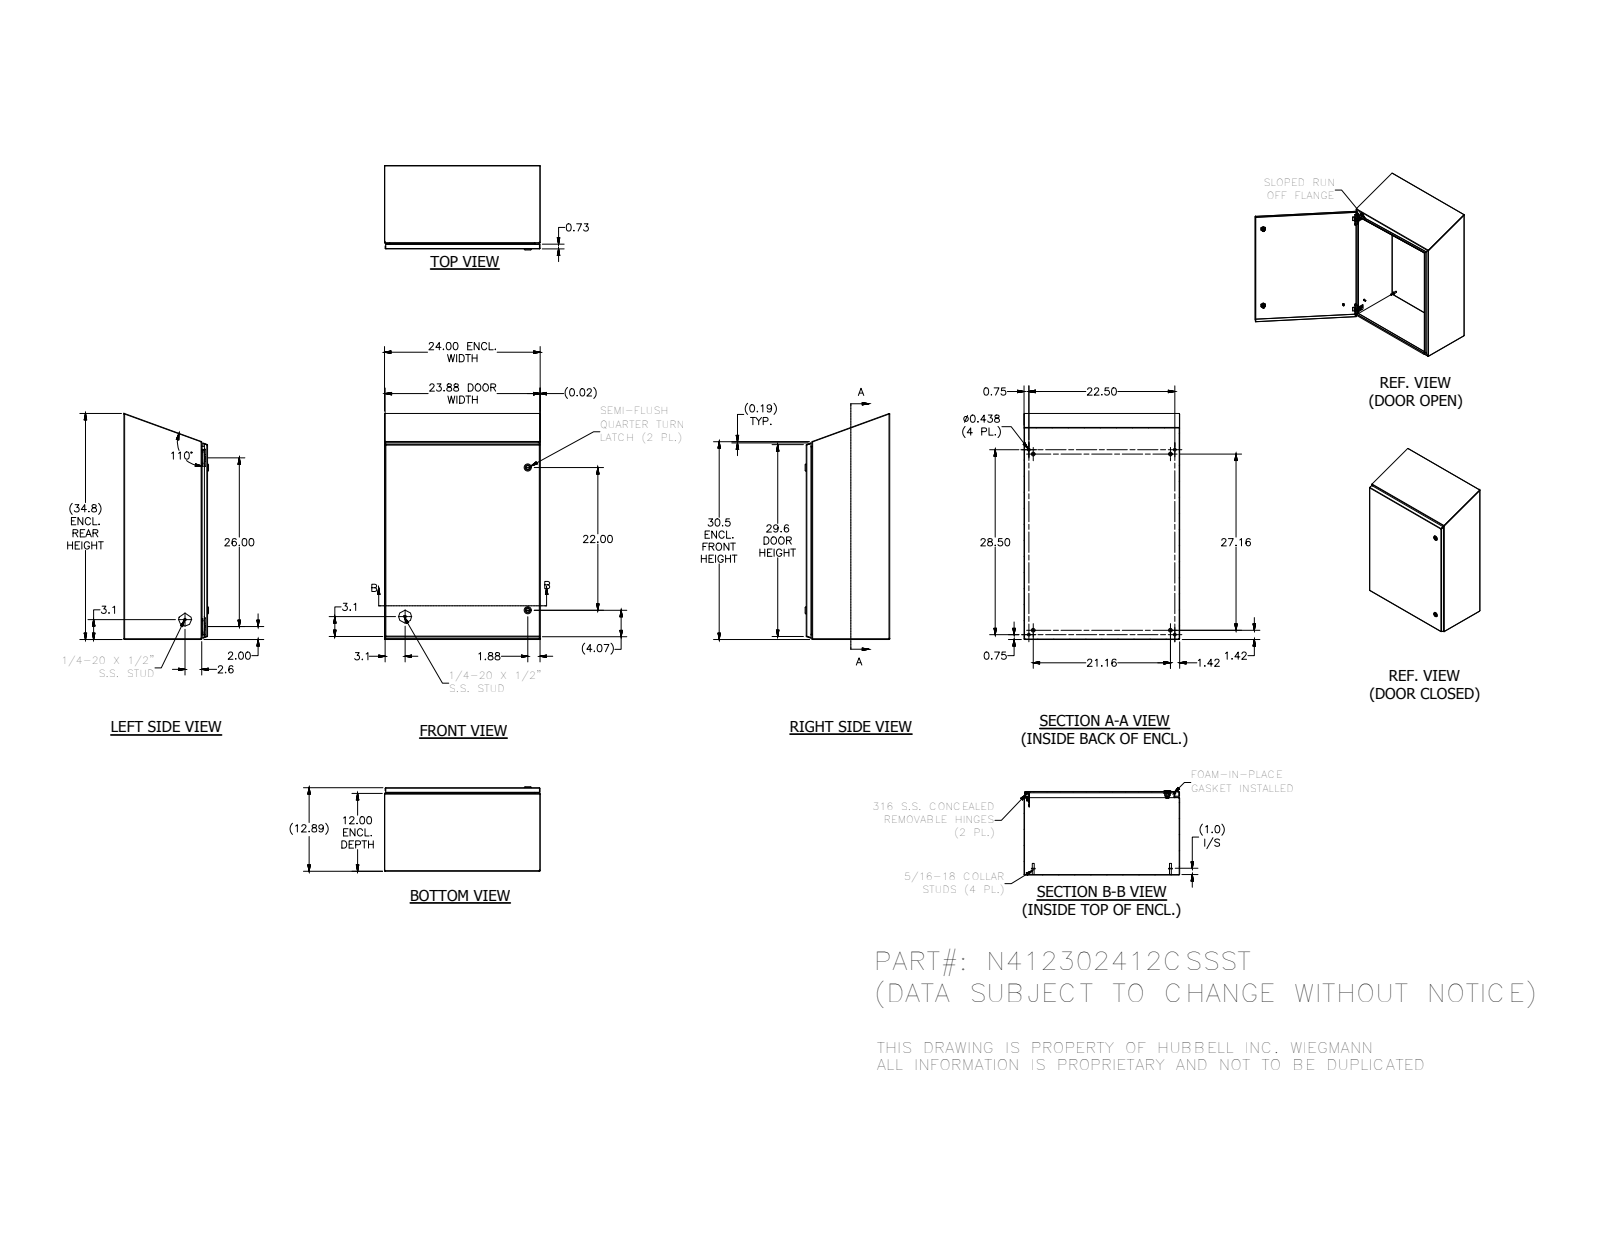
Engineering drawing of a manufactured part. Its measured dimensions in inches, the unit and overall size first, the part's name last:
Units: inches
Overall size (bounding box): 34.847 × 24 × 13.044
Round holes (diameter × count): ⌀0.093 ×4, ⌀0.152 ×4, ⌀0.167 ×4, ⌀0.172 ×4, ⌀0.187 ×4, ⌀0.437 ×4, ⌀0.156 ×3, ⌀0.197 ×2, ⌀0.315 ×2, ⌀0.394 ×2, ⌀0.402 ×2, ⌀0.634 ×2
Round bosses / shafts (diameter × count): ⌀0.25 ×10, ⌀0.563 ×4, ⌀0.36 ×4, ⌀0.32 ×4, ⌀0.3 ×4, ⌀0.275 ×4, ⌀0.256 ×4, ⌀0.164 ×4
Partial cylindrical surfaces — rounded edges, fillets, slot ends (radius × count): R0.031 ×29, R0.05 ×26, R0.02 ×24, R0.105 ×19, R0.016 ×18, R0.125 ×16, R0.032 ×8, R0.177 ×6
Main face-to-face distances: 0.074, 12.813, 23.926, 12.887, 12.739, 23.852, 24, 11.926, 0.887, 0.813
Hole centre spacings: 26, 22.8, 0.5, 0.656, 0.66, 0.952, 1.307, 1.311
Volume: 233.5 in³ · Surface area: 6 347 in²
Bodies: 42 solids, 1732 faces (717 planar, 604 cylindrical, 411 other)
Part name (STEP PRODUCT): N412_CSSST-assm; N412302412CSSSTB3S; HFW3161; HFW328176 (+8 more)
STEP written by: Autodesk Inventor 2012 (AUTOMOTIVE_DESIGN)
